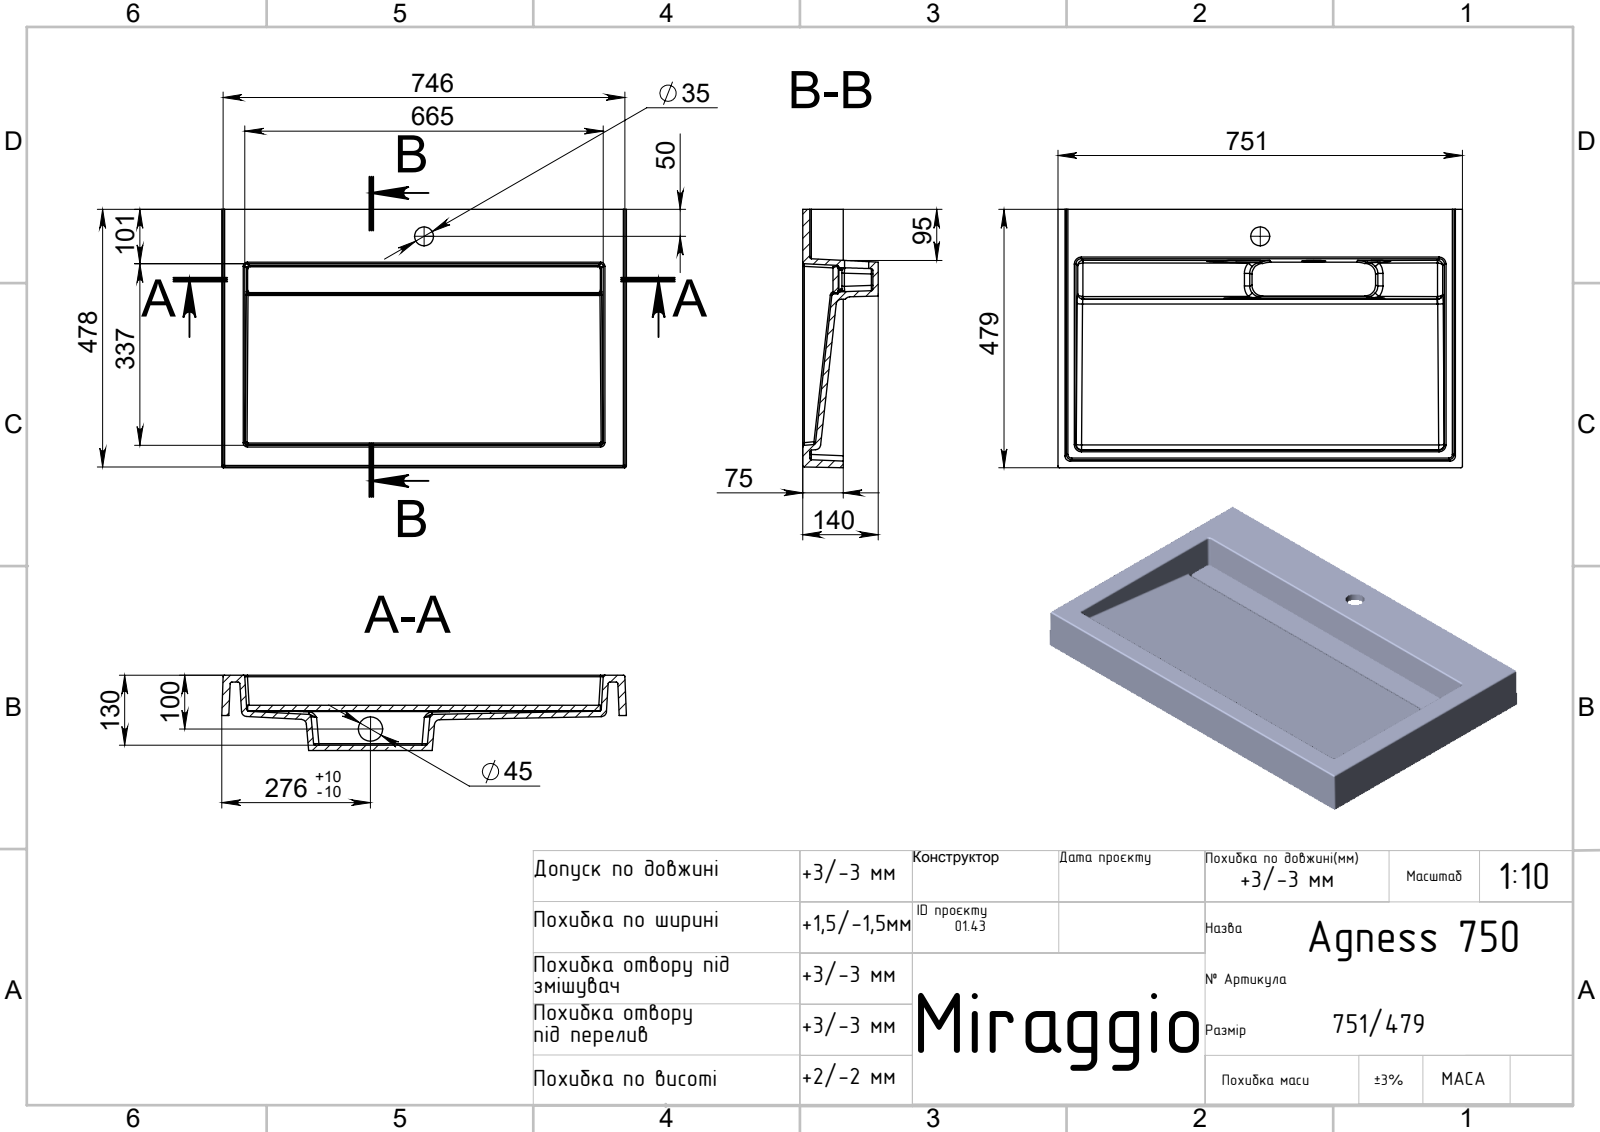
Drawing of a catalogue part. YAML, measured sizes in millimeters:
part_name: "Agness 750"
step_written_by: "SolidWorks 2020 (AUTOMOTIVE_DESIGN)"
units: millimeters
bodies: {solids: 2, faces: 218, planar: 48, cylindrical: 81, other: 89}
overall_size: [751, 479.26, 140]
volume: 6898000
surface_area: 1255000
round_holes:
  - {diameter: 35, count: 1}
  - {diameter: 45, count: 1}
partial_cylinders:
  - {radius: 3, count: 24}
  - {radius: 5, count: 22}
  - {radius: 10, count: 21}
  - {radius: 1.5, count: 6}
  - {radius: 20, count: 4}
face_to_face_distances: [10, 13, 53, 66, 43, 56, 9, 19, 62, 75]
